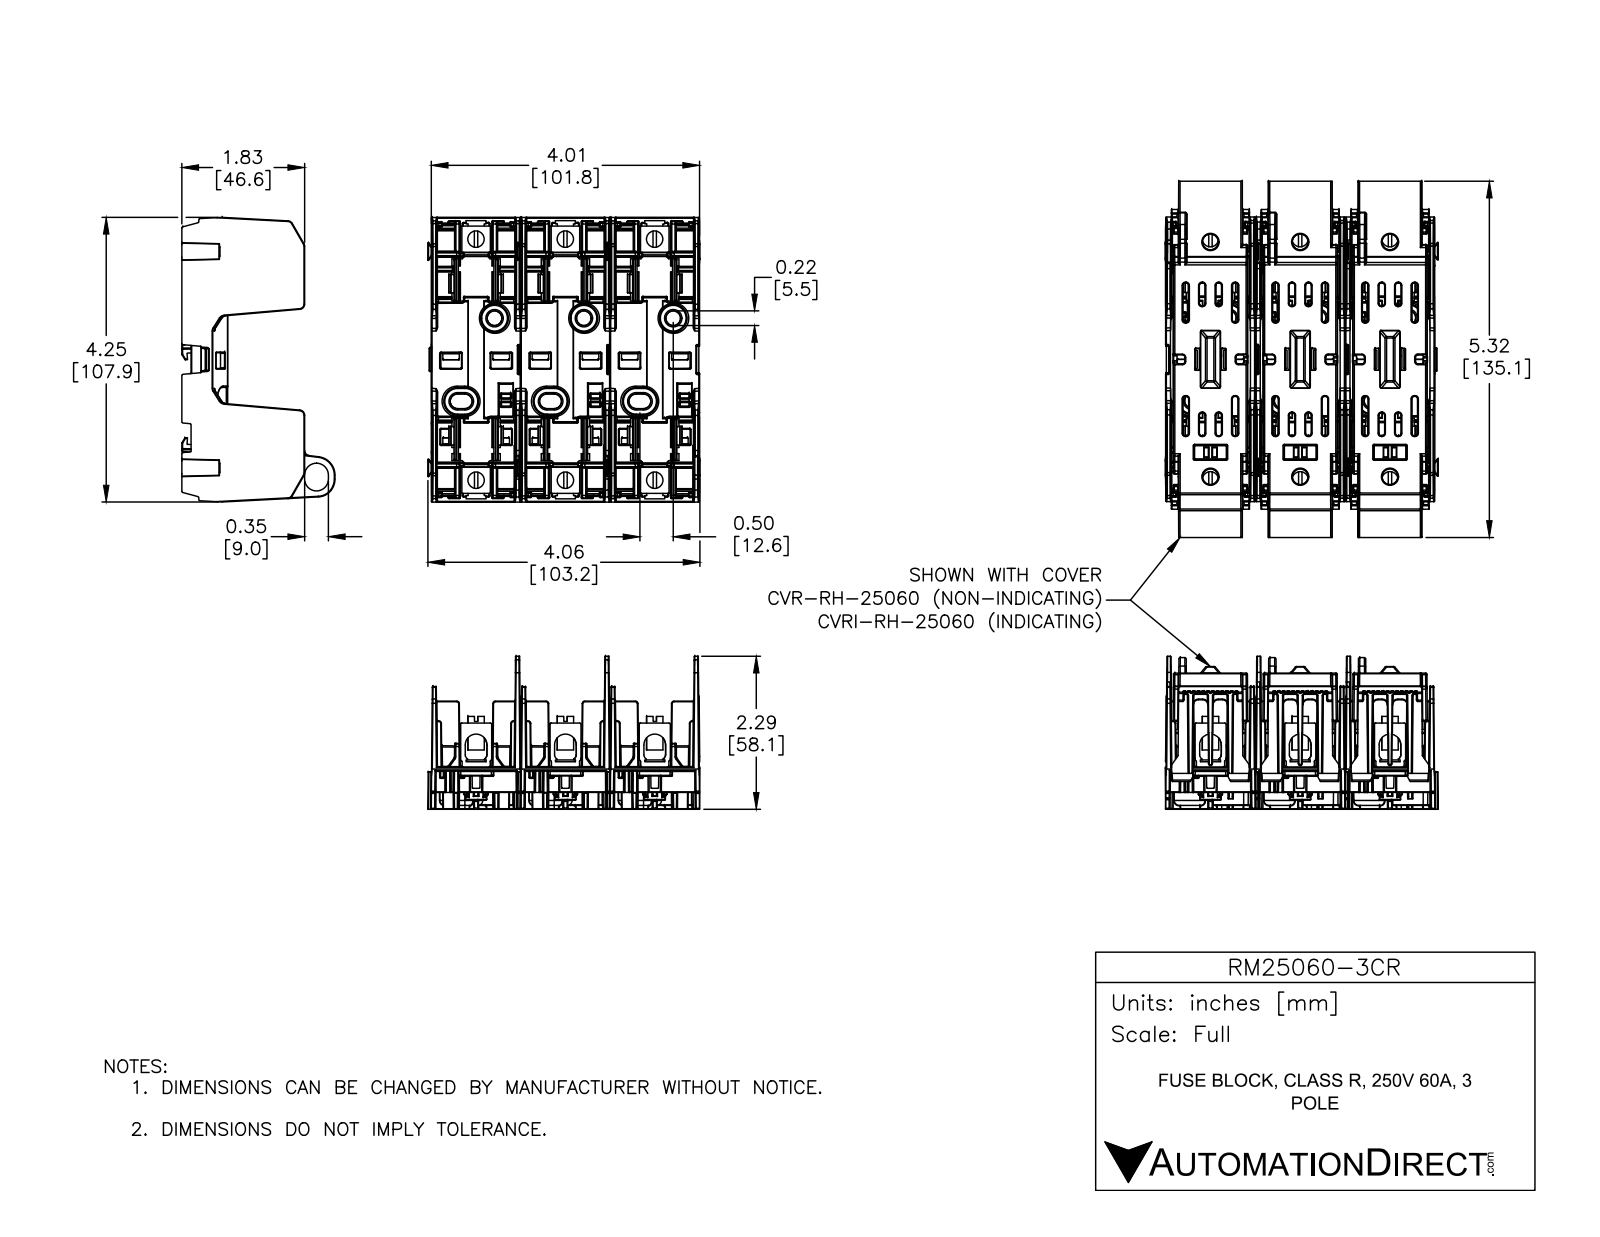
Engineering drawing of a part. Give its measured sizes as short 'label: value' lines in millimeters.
name: RM25060-3CR; RM25060-1CR
written by: SolidWorks 2016 (AUTOMOTIVE_DESIGN)
unit: mm
bodies: 39 solids, 1182 faces (684 planar, 498 cylindrical, 0 other)
size: 105.5 × 95.4 × 26.9
volume: 14 600 mm³; area: 32 300 mm²
holes: 6× ⌀5.7, 6× ⌀6.2
bosses: 6× ⌀6.2
rounds: 76× R0.3, 48× R0.5, 30× R1, 24× R0.5, 18× R1.5, 12× R1.8, 12× R2, 12× R2.2
face distances: 0.7, 0.6, 34, 34, 68, 34, 1.4, 34, 1.3, 67.9
hole spacings: 34, 37.1, 37.1, 68, 70.6, 83.8, 14.8, 14.8
